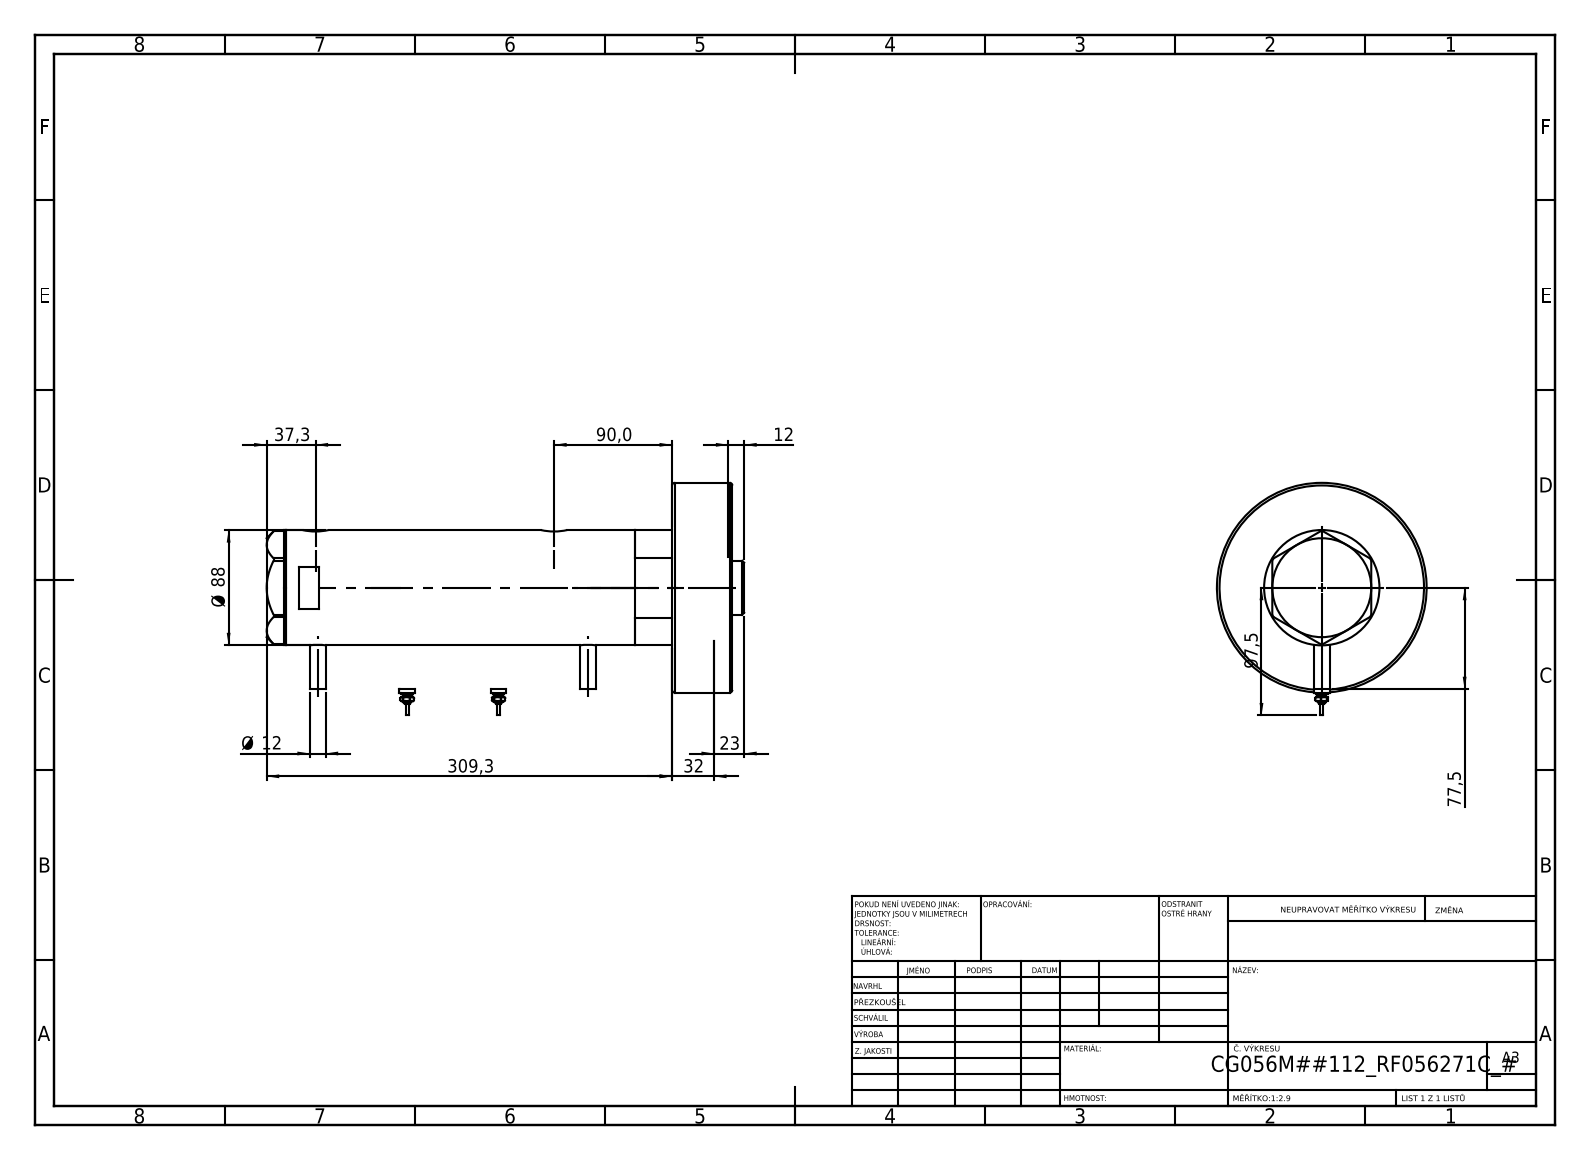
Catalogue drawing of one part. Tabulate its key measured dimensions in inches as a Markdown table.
| quantity | value |
| --- | --- |
| part name | V270CG_MIDDLE; V270CG_FRONT; V270CG_BACK; V270CG_VC (+2 more) |
| STEP written by | SolidWorks 2019 (CONFIG_CONTROL_DESIGN) |
| units | inches |
| bodies | 7 solids, 223 faces (82 planar, 73 cylindrical, 68 other) |
| overall size | 14.343 × 6.988 × 6.299 |
| volume | 159.9 in³ |
| surface area | 512 in² |
| round holes (diameter × count) | 0.492 × 2, 0.518 × 2, 0.787 × 2, 0.571 × 1, 1.654 × 1, 1.713 × 1, 2.205 × 1, 2.362 × 1, 2.953 × 1, 3.15 × 1 |
| round bosses / shafts (diameter × count) | 0.472 × 4, 0.354 × 2, 0.276 × 2, 0.177 × 2, 0.098 × 2, 6.299 × 1, 3.465 × 1, 2.874 × 1 |
| main face-to-face distances | 1.811, 11.587, 13.398, 8.047, 3.539, 5.35, 12.374, 1.024, 7.024, 10.563 |
| hole center spacings | 0.067, 1.016, 7.098, 7.165, 8.114, 8.181 |
